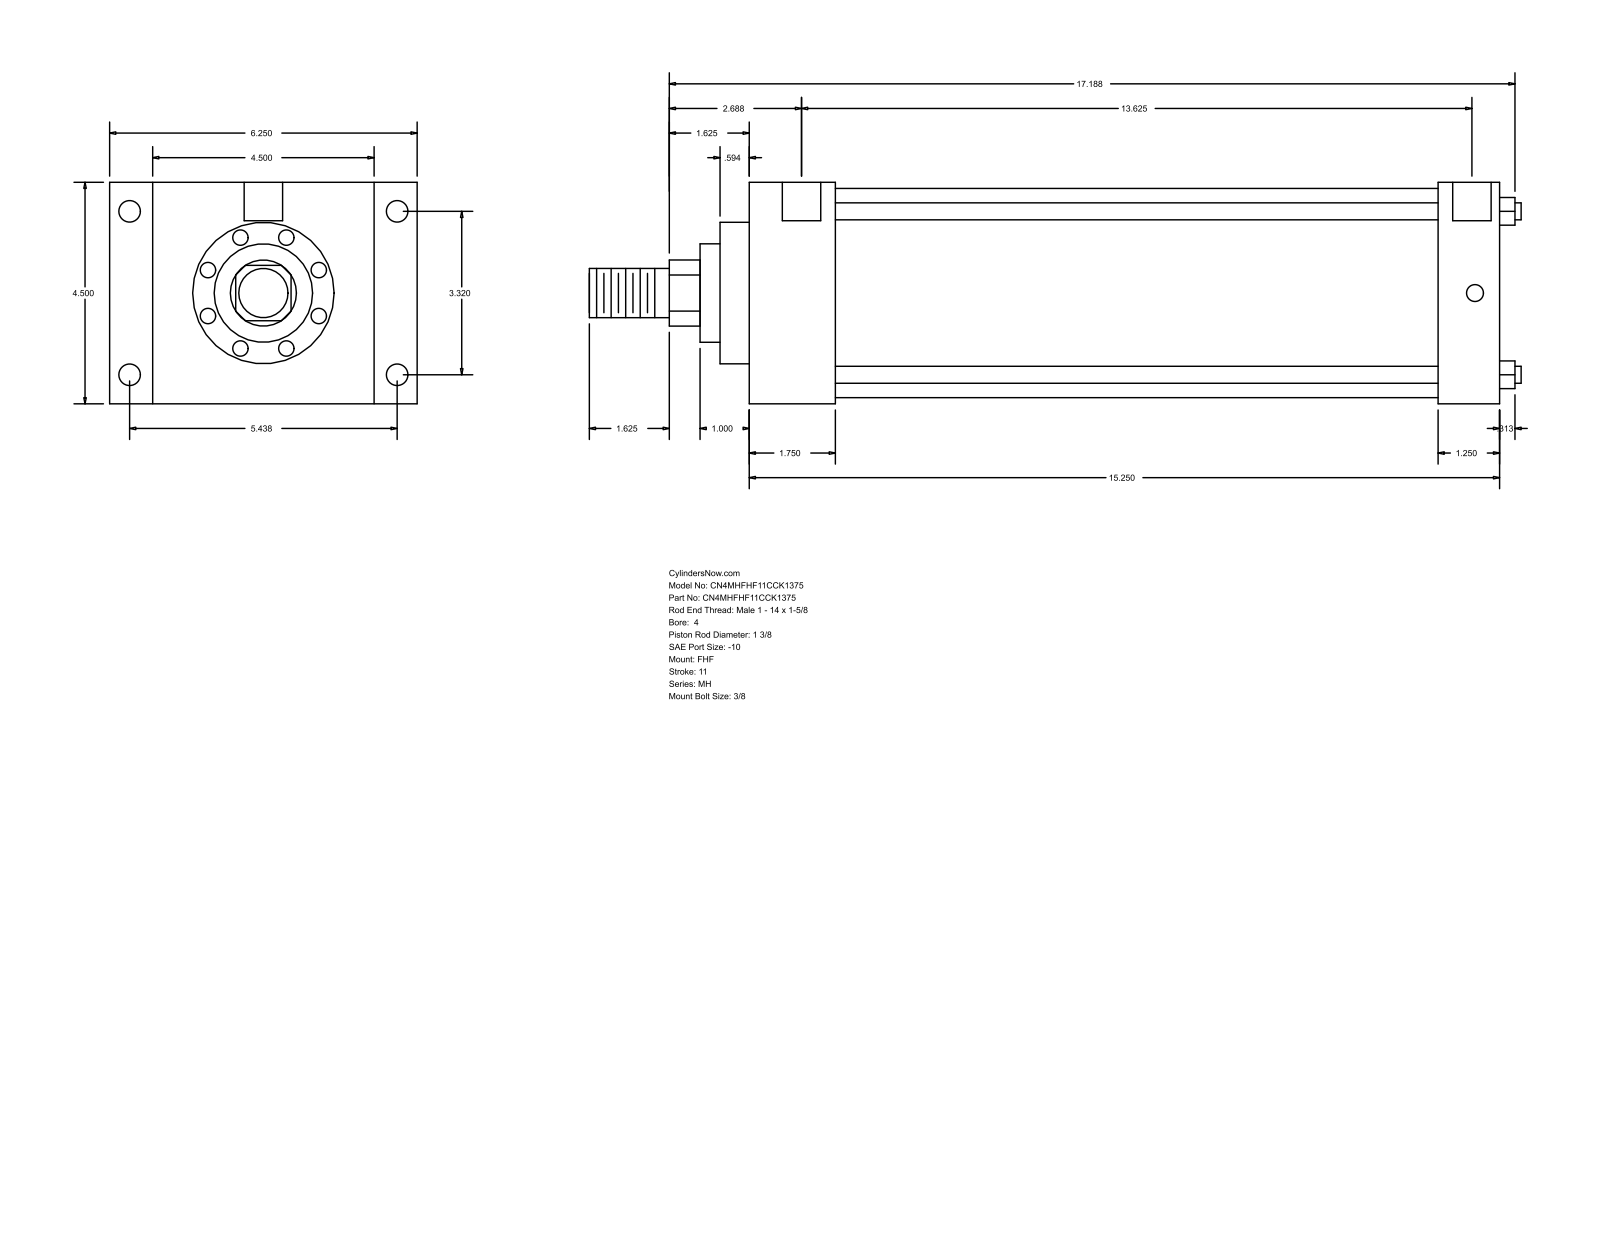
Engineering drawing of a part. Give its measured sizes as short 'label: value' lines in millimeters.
name: MH_FHF__0400_1.375
written by: GSSL Pune (CONFIG_CONTROL_DESIGN)
unit: mm
bodies: 0 solids, 90 faces (61 planar, 29 cylindrical, 0 other)
size: 481.01 × 158.75 × 114.3
holes: 4× ⌀8.73, 4× ⌀11.13, 2× ⌀19.84
bosses: 4× ⌀8.76, 1× ⌀107.95, 1× ⌀73.03, 1× ⌀50.8, 1× ⌀34.92, 1× ⌀25.4
rounds: 1× R17.06
face distances: 114.3, 387.35, 44.45, 342.9, 22.23, 136.53, 158.76, 355.61, 311.16, 31.74
hole spacings: 1.59, 84.32, 138.12, 161.82, 347.67, 349.26, 346.08
